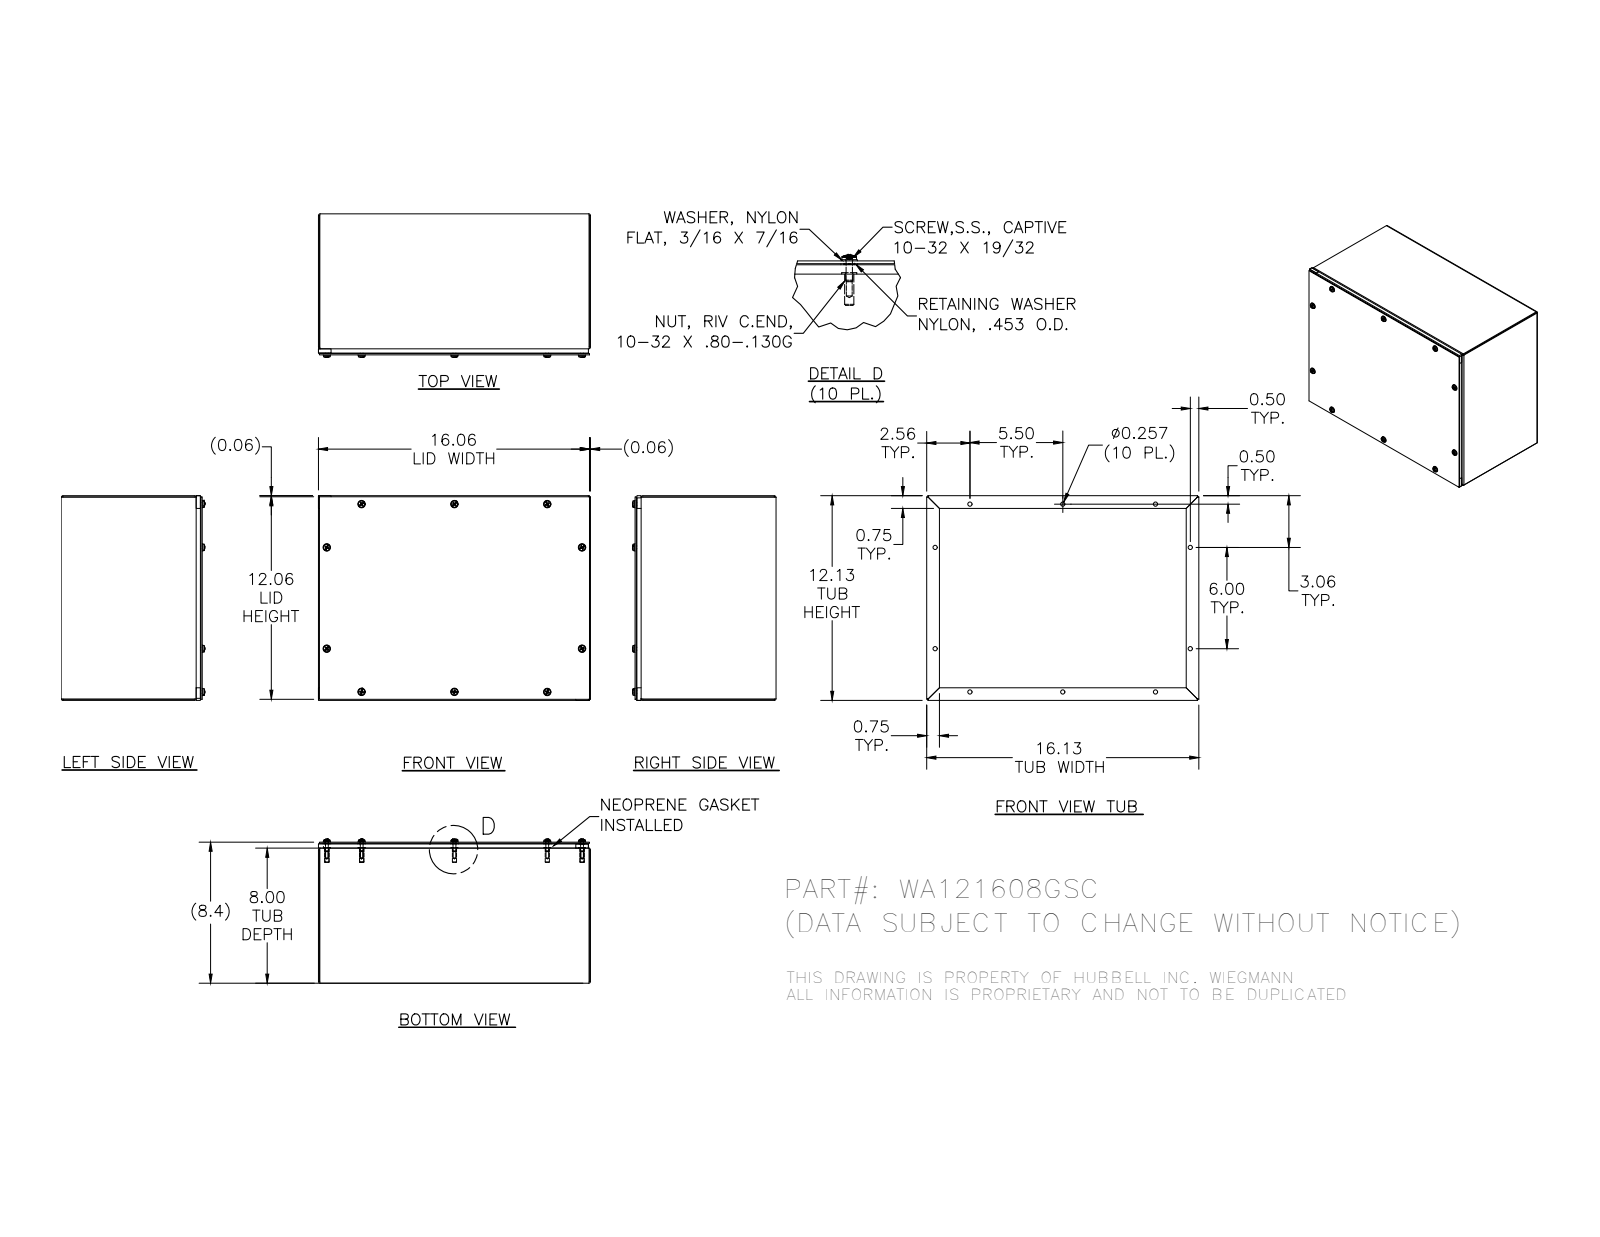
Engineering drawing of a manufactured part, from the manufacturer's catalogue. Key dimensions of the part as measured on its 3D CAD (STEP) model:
Part name (STEP PRODUCT): WA1216GSC_LP; WA121608GSC; 34984; 37210 (+3 more)
STEP written by: SolidWorks 2014 (AUTOMOTIVE_DESIGN)
Units: inches
Bodies: 45 solids, 1064 faces (502 planar, 276 cylindrical, 286 other)
Overall size (bounding box): 16.125 × 12.125 × 8.511
Volume: 72.67 in³ · Surface area: 1 854 in²
Round holes (diameter × count): ⌀0.188 ×10, ⌀0.257 ×10, ⌀0.278 ×10, ⌀0.281 ×10, ⌀0.156 ×9, ⌀0.196 ×9
Round bosses / shafts (diameter × count): ⌀0.453 ×10, ⌀0.437 ×10, ⌀0.167 ×10, ⌀0.406 ×9, ⌀0.248 ×9
Partial cylindrical surfaces — rounded edges, fillets, slot ends (radius × count): R0.089 ×10, R0.031 ×8, R0.105 ×8
Main face-to-face distances: 0.074, 8.282, 12.051, 8.356, 8.208, 16.051, 12.125, 11.977, 0.356, 7.926
Hole centre spacings: 5.5, 11.424, 3.289, 6, 7.985, 8.807, 11, 13.311
